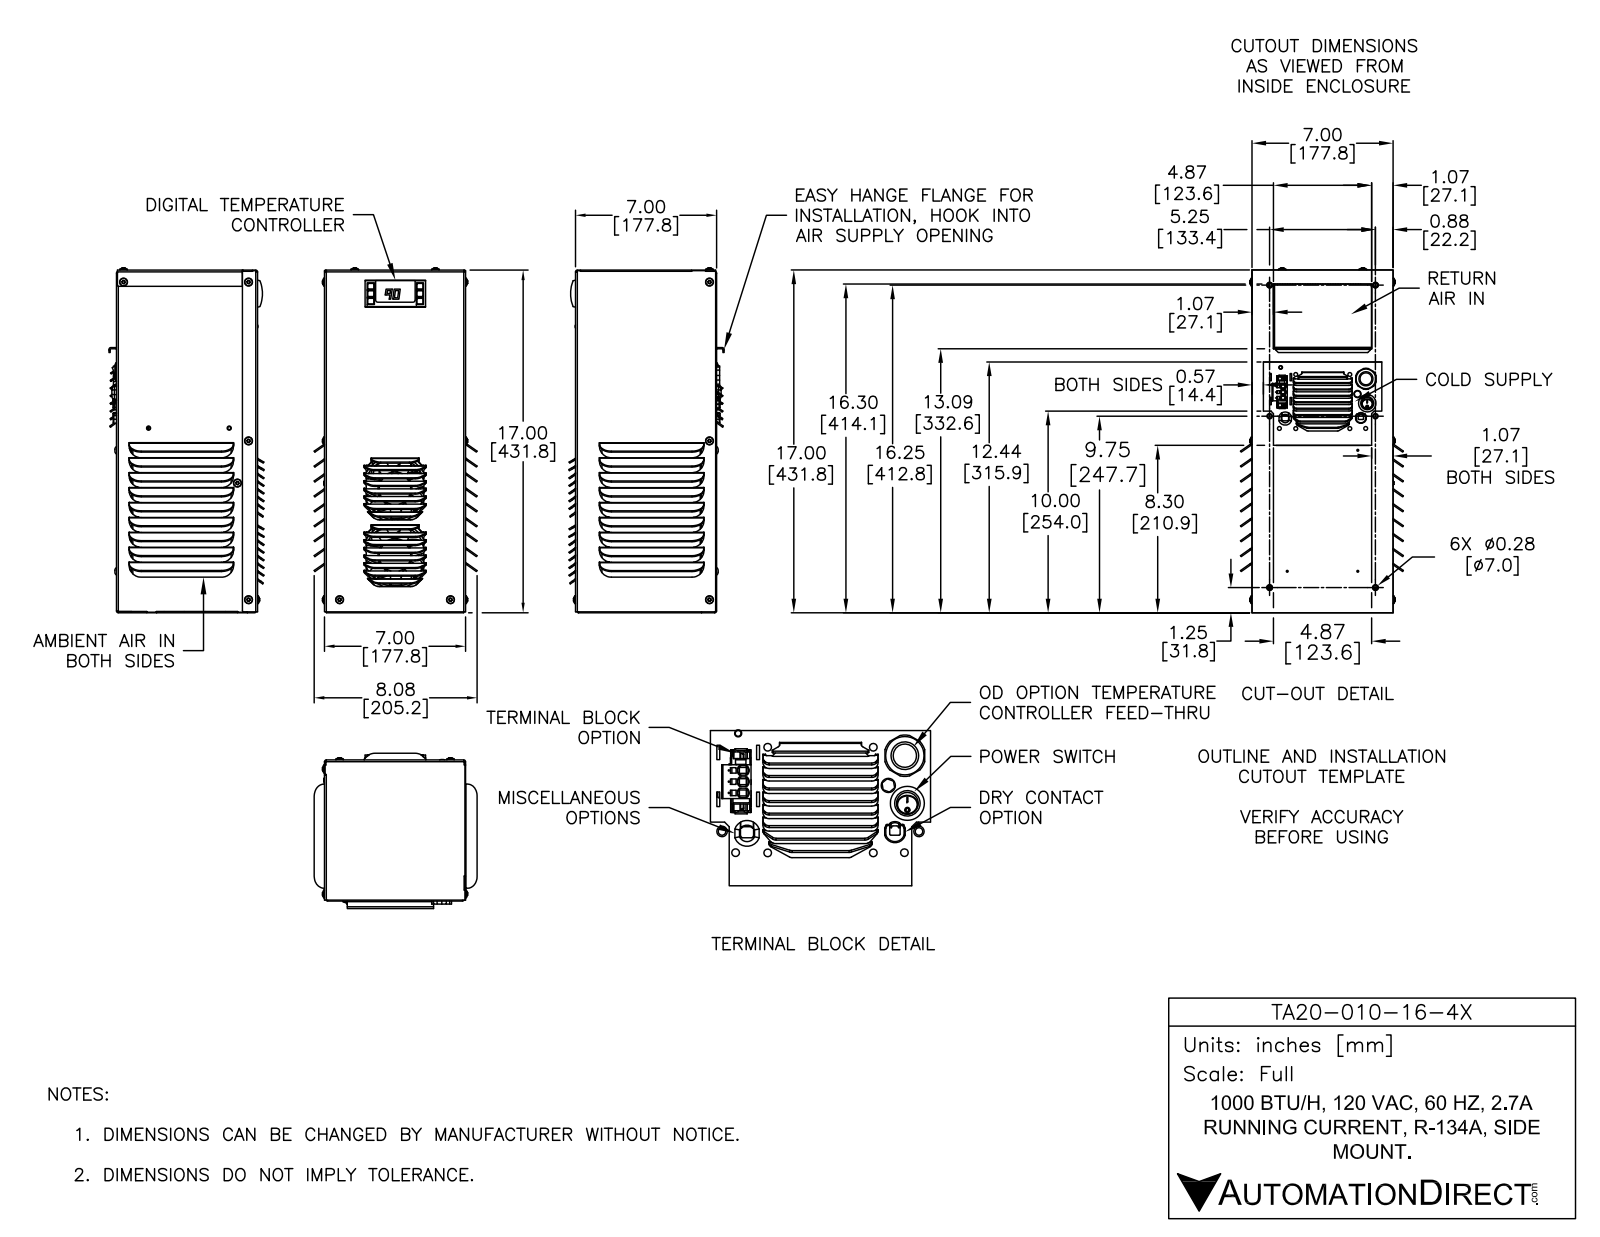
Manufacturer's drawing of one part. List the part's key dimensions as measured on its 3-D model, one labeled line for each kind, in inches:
Part name (STEP PRODUCT): TA20-010-16-4X
STEP written by: SolidWorks 2019 (AUTOMOTIVE_DESIGN)
Units: inches
Bodies: 70 solids, 3570 faces (1682 planar, 1401 cylindrical, 487 other)
Overall size (bounding box): 17.092 × 8.079 × 7.704
Volume: 93.28 in³ · Surface area: 1 758 in²
Round holes (diameter × count): ⌀0.203 ×16, ⌀0.325 ×16, ⌀0.33 ×16, ⌀0.28 ×14, ⌀0.219 ×10, ⌀0.193 ×8, ⌀0.2 ×6, ⌀0.201 ×6, ⌀0.272 ×6, ⌀0.109 ×5, ⌀0.195 ×4, ⌀0.156 ×2
Round bosses / shafts (diameter × count): ⌀0.19 ×17, ⌀0.329 ×14, ⌀0.313 ×10, ⌀0.564 ×6, ⌀0.44 ×6, ⌀0.344 ×6, ⌀0.326 ×6, ⌀0.321 ×6
Partial cylindrical surfaces — rounded edges, fillets, slot ends (radius × count): R0.01 ×100, R0.125 ×91, R0.005 ×90, R0.031 ×81, R0.015 ×77, R0.091 ×57, R0.03 ×53, R0.594 ×36
Main face-to-face distances: 0.06, 6.938, 0.06, 6.998, 6.935, 6.875, 6.875, 6.815, 6.878, 16.938
Hole centre spacings: 0.8, 1, 1.601, 1.625, 1.25, 2, 2.359, 1.94
